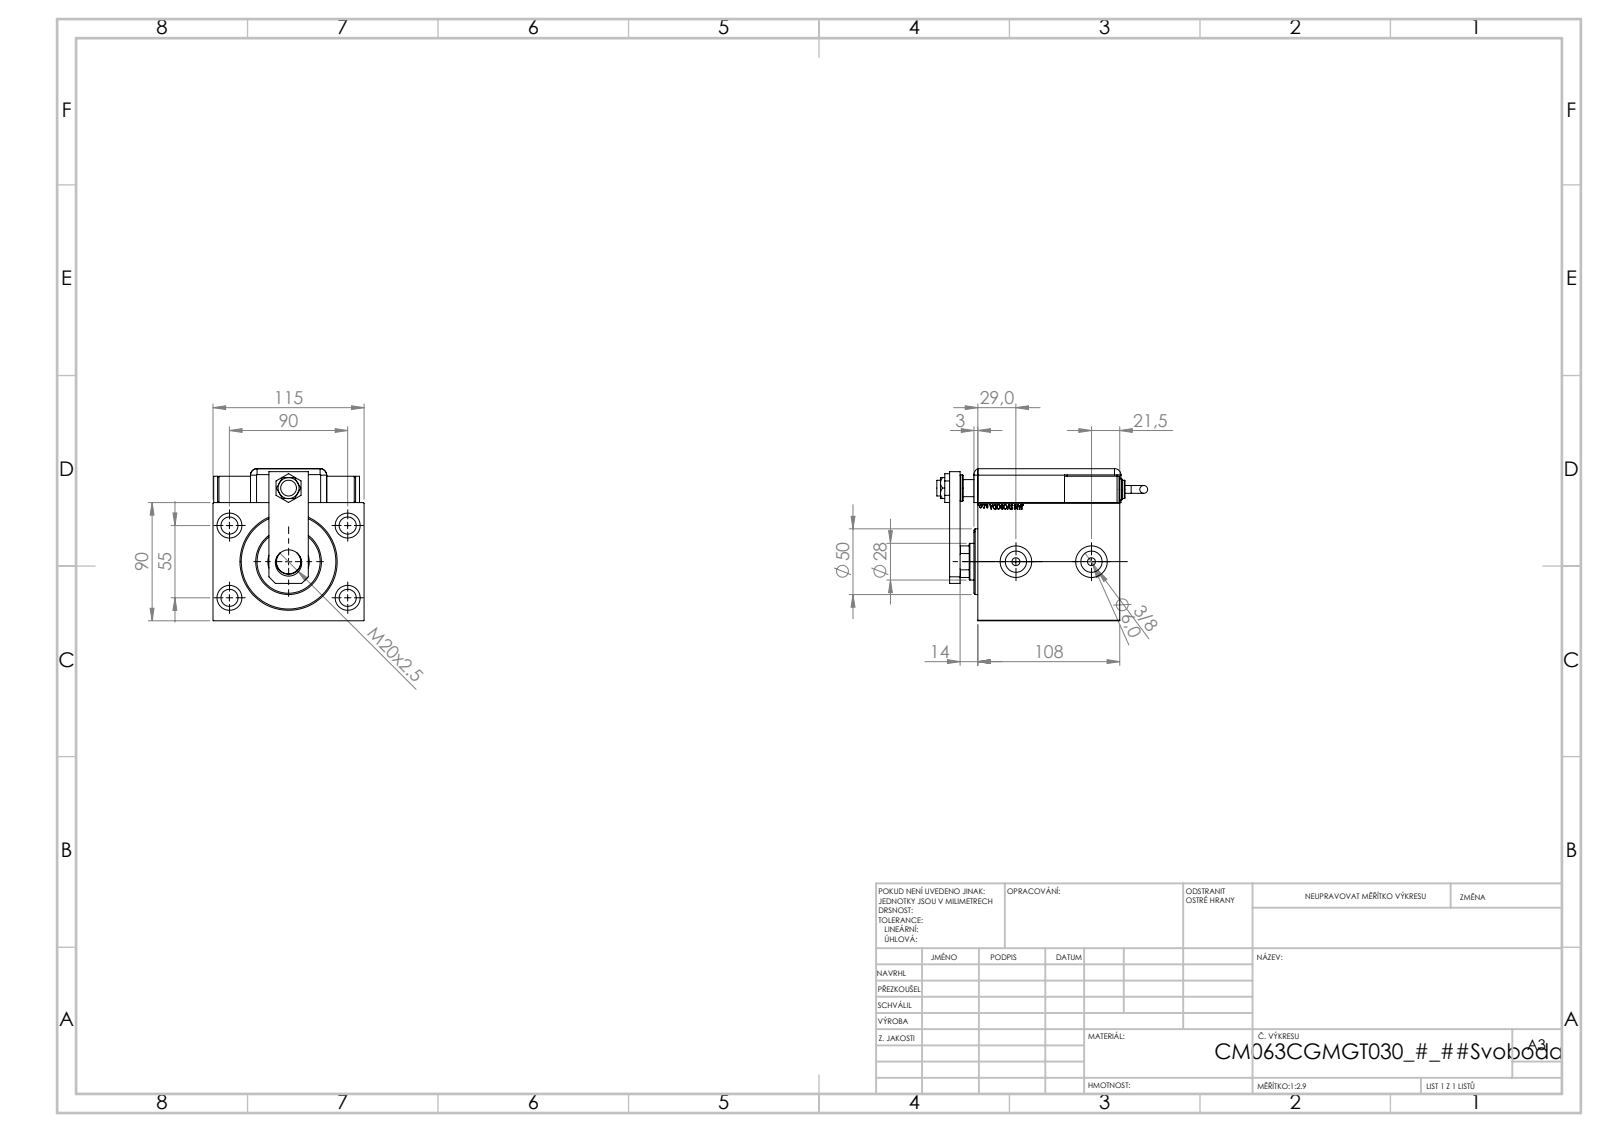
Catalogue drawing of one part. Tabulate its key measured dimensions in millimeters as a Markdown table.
| quantity | value |
| --- | --- |
| part name | TYC; SWITCH_Q_FRONT_BACK; SWITCH DIM A_G; NUT_D13 (+7 more) |
| STEP written by | SolidWorks 2019 (CONFIG_CONTROL_DESIGN) |
| units | millimeters |
| bodies | 13 solids, 1249 faces (615 planar, 117 cylindrical, 517 other) |
| overall size | 160.46 × 115.8 × 115 |
| volume | 1 116 000 mm³ |
| surface area | 194 215 mm² |
| round holes (diameter × count) | 13 × 5, 19 × 4, 4 × 2, 6 × 2, 8 × 2, 16.17 × 2, 24 × 2, 12 × 1, 14 × 1, 18.5 × 1, 20 × 1, 28 × 1 |
| round bosses / shafts (diameter × count) | 20 × 3, 16 × 2, 14 × 2, 6 × 2, 50 × 1 |
| partial cylindrical surfaces (radius × count) | 5 × 9, 10 × 1, 13.5 × 1 |
| main face-to-face distances | 90, 3, 108, 115, 90.5, 17.5, 13.5, 8, 25.8, 115.8 |
| hole center spacings | 52.74, 53.27, 52.22, 55, 90, 94.85, 105.48, 1 |
